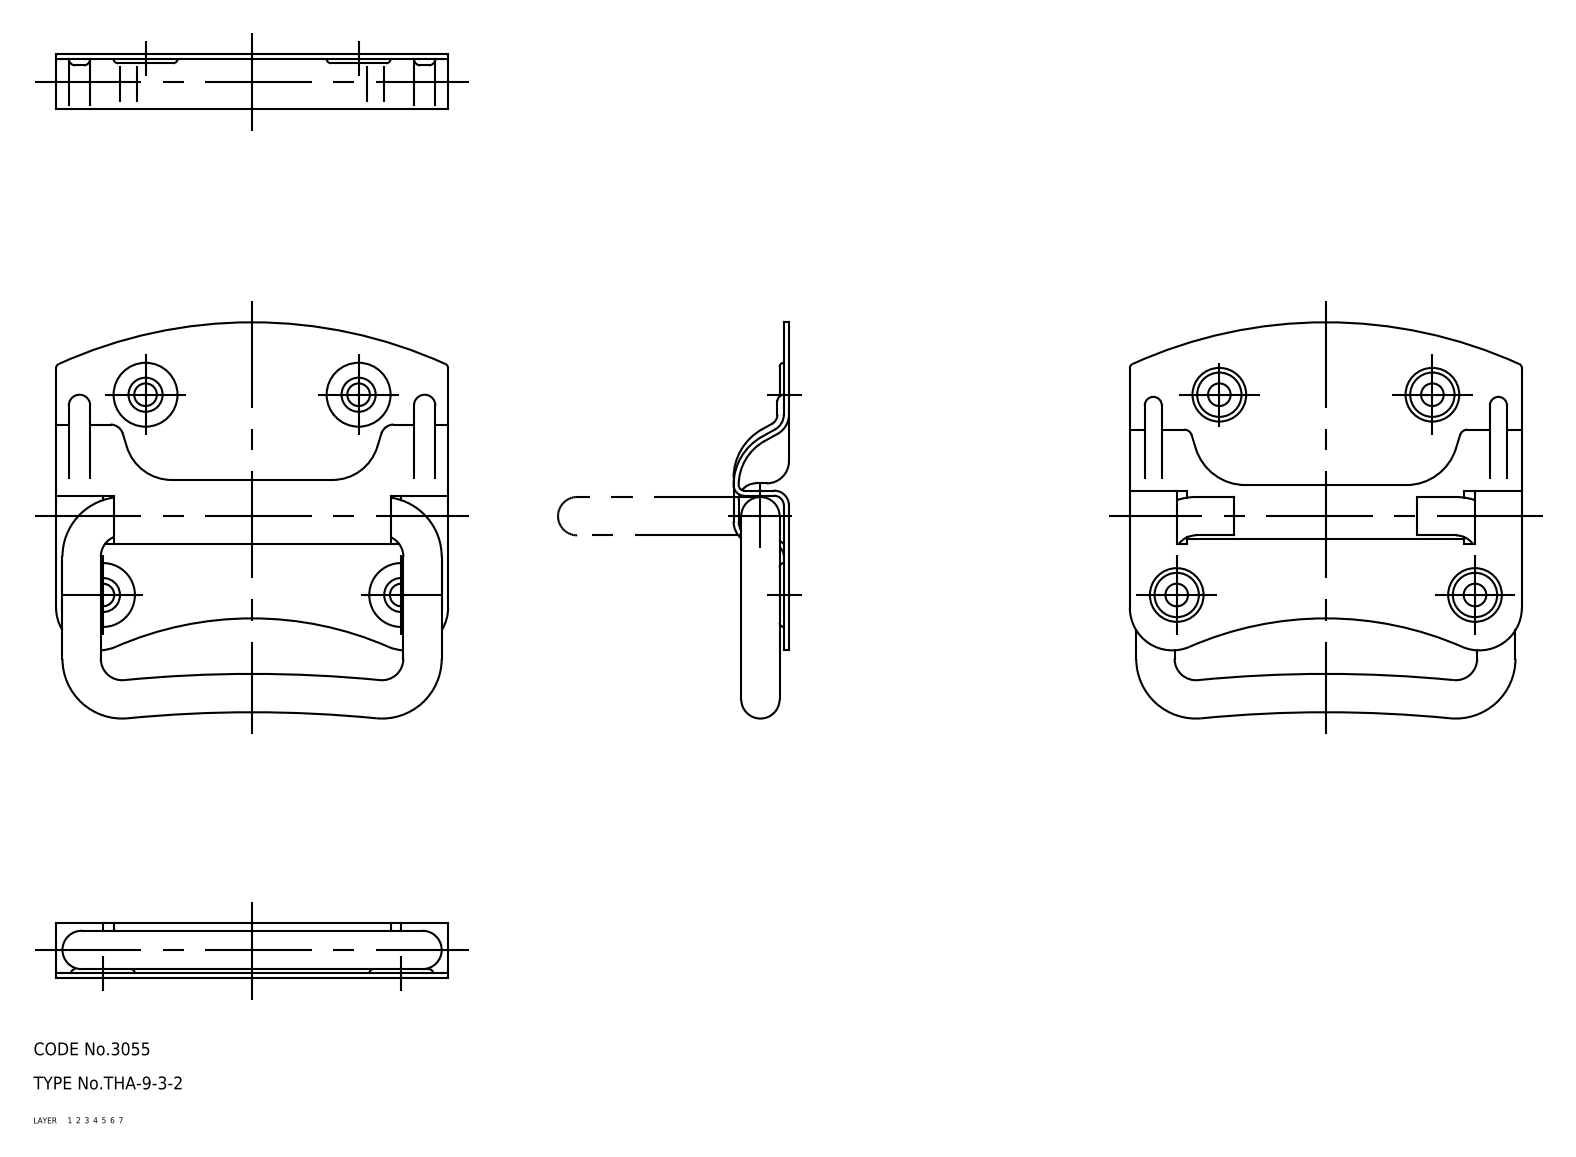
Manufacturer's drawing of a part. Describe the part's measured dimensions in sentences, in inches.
The part is named "grip; base; THA_9_3_2_3852_36". Its 3-D file was written by "CADfix (AUTOMOTIVE_DESIGN)". It is 2 solids with 286 faces: 0 planar, 0 cylindrical and 286 other. Overall it measures 3.661 by 3.622 by 0.512 inches. Its volume is 1.285 cubic inches and its surface area 33.82 square inches.
